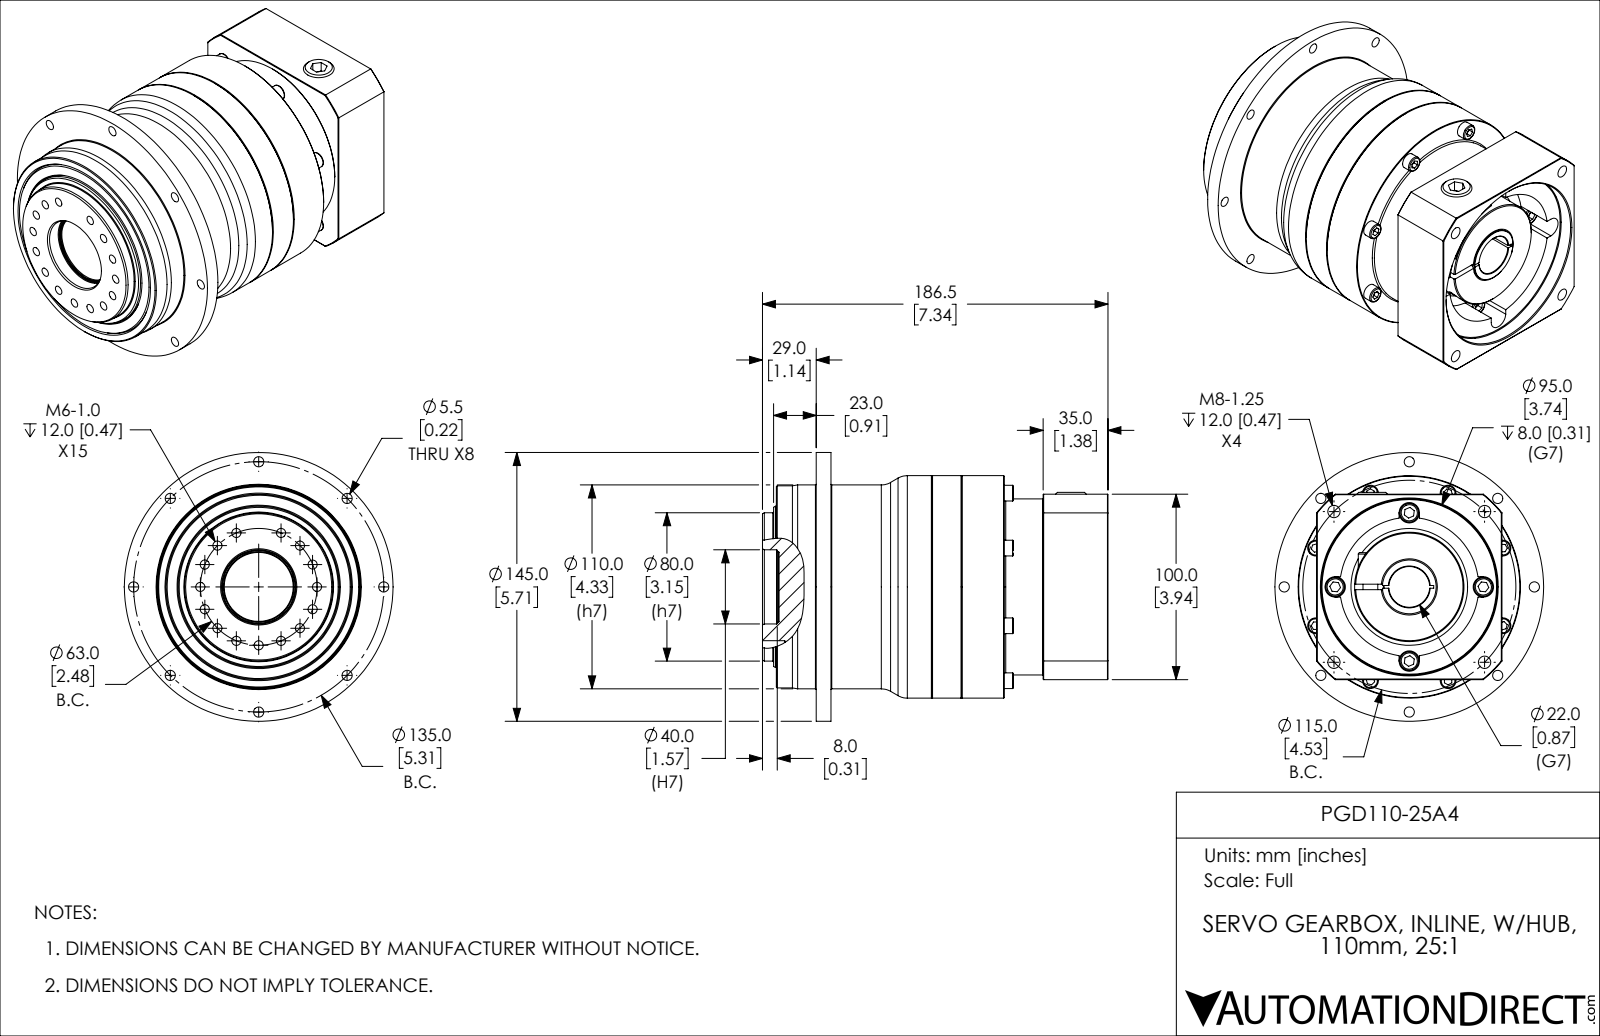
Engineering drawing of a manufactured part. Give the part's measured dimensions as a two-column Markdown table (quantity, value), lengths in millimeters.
| quantity | value |
| --- | --- |
| part name | PGD110-25A4 |
| STEP written by | SolidWorks 2015 (AUTOMOTIVE_DESIGN) |
| units | millimeters |
| bodies | 12 solids, 497 faces (240 planar, 180 cylindrical, 77 other) |
| overall size | 186.5 × 145 × 145 |
| volume | 1 702 000 mm³ |
| surface area | 149 396 mm² |
| round holes (diameter × count) | 4.92 × 11, 5.5 × 8, 4.92 × 4, 6.65 × 3, 6.65 × 1, 8.8 × 1, 13 × 1, 15 × 1, 22 × 1, 37.2 × 1, 39.2 × 1, 61 × 1 |
| round bosses / shafts (diameter × count) | 8.5 × 8, 10 × 4, 8 × 2, 145 × 1, 120 × 1, 110 × 1, 80 × 1, 54.5 × 1 |
| partial cylindrical surfaces (radius × count) | 5.5 × 4, 7 × 1, 64 × 1 |
| main face-to-face distances | 4, 22, 26, 7, 151.5, 100, 145.5, 140.5, 20, 149.5 |
| hole center spacings | 40.25, 62.62, 84.71, 97.35, 12.29, 52.38, 74.49, 44.54 |
